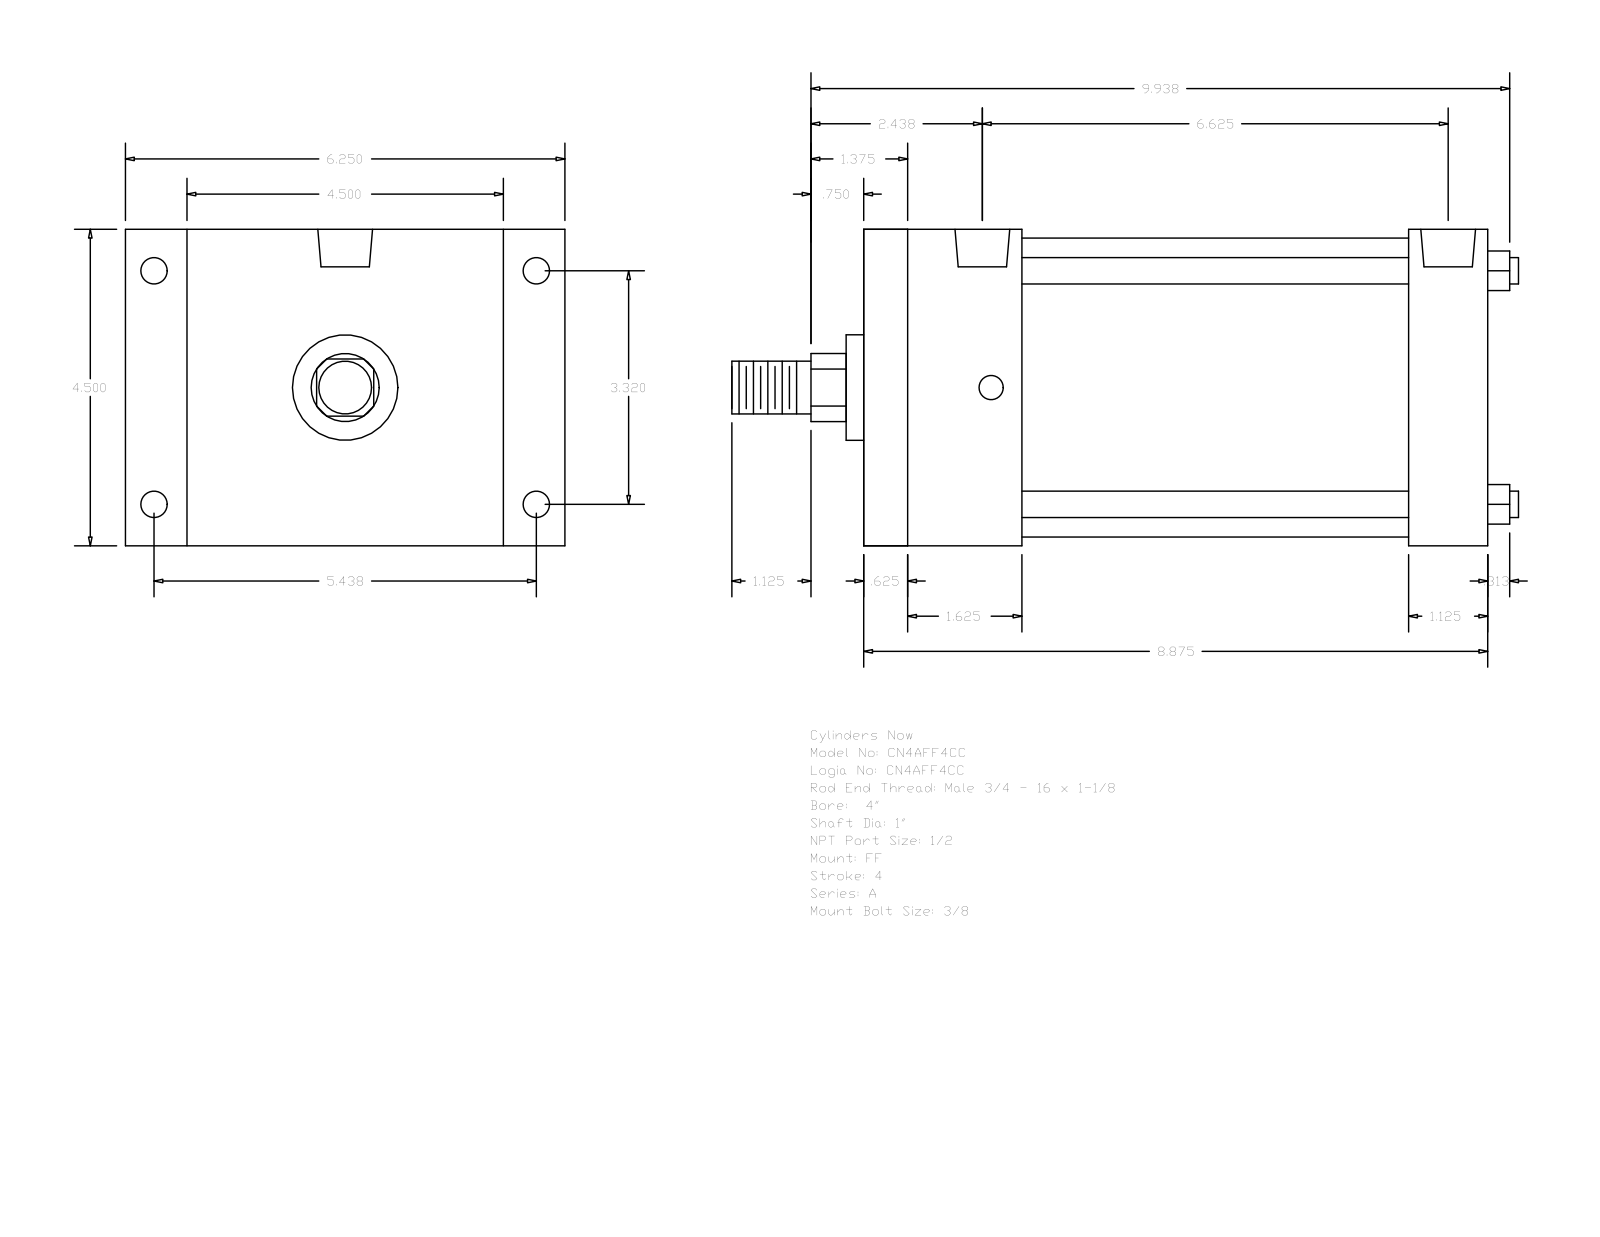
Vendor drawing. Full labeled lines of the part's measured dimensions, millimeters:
Part name (STEP PRODUCT): A_FF__0400_1
STEP written by: GSSL Pune (CONFIG_CONTROL_DESIGN)
Units: millimetres
Bodies: 0 solids, 92 faces (64 planar, 28 cylindrical, 0 other)
Overall size (bounding box): 284.16 × 158.75 × 114.3
Round holes (diameter × count): ⌀8.73 ×4, ⌀9.53 ×4, ⌀19.77 ×2
Round bosses / shafts (diameter × count): ⌀9.53 ×4, ⌀107.95 ×1, ⌀38.1 ×1, ⌀25.4 ×1, ⌀19.05 ×1
Partial cylindrical surfaces — rounded edges, fillets, slot ends (radius × count): R12.29 ×1
Main face-to-face distances: 114.3, 225.42, 15.87, 209.55, 28.57, 22.23, 136.53, 196.85, 180.98, 57.15
Hole centre spacings: 3.18, 84.32, 138.12, 161.82, 161.92, 165.1, 168.28
